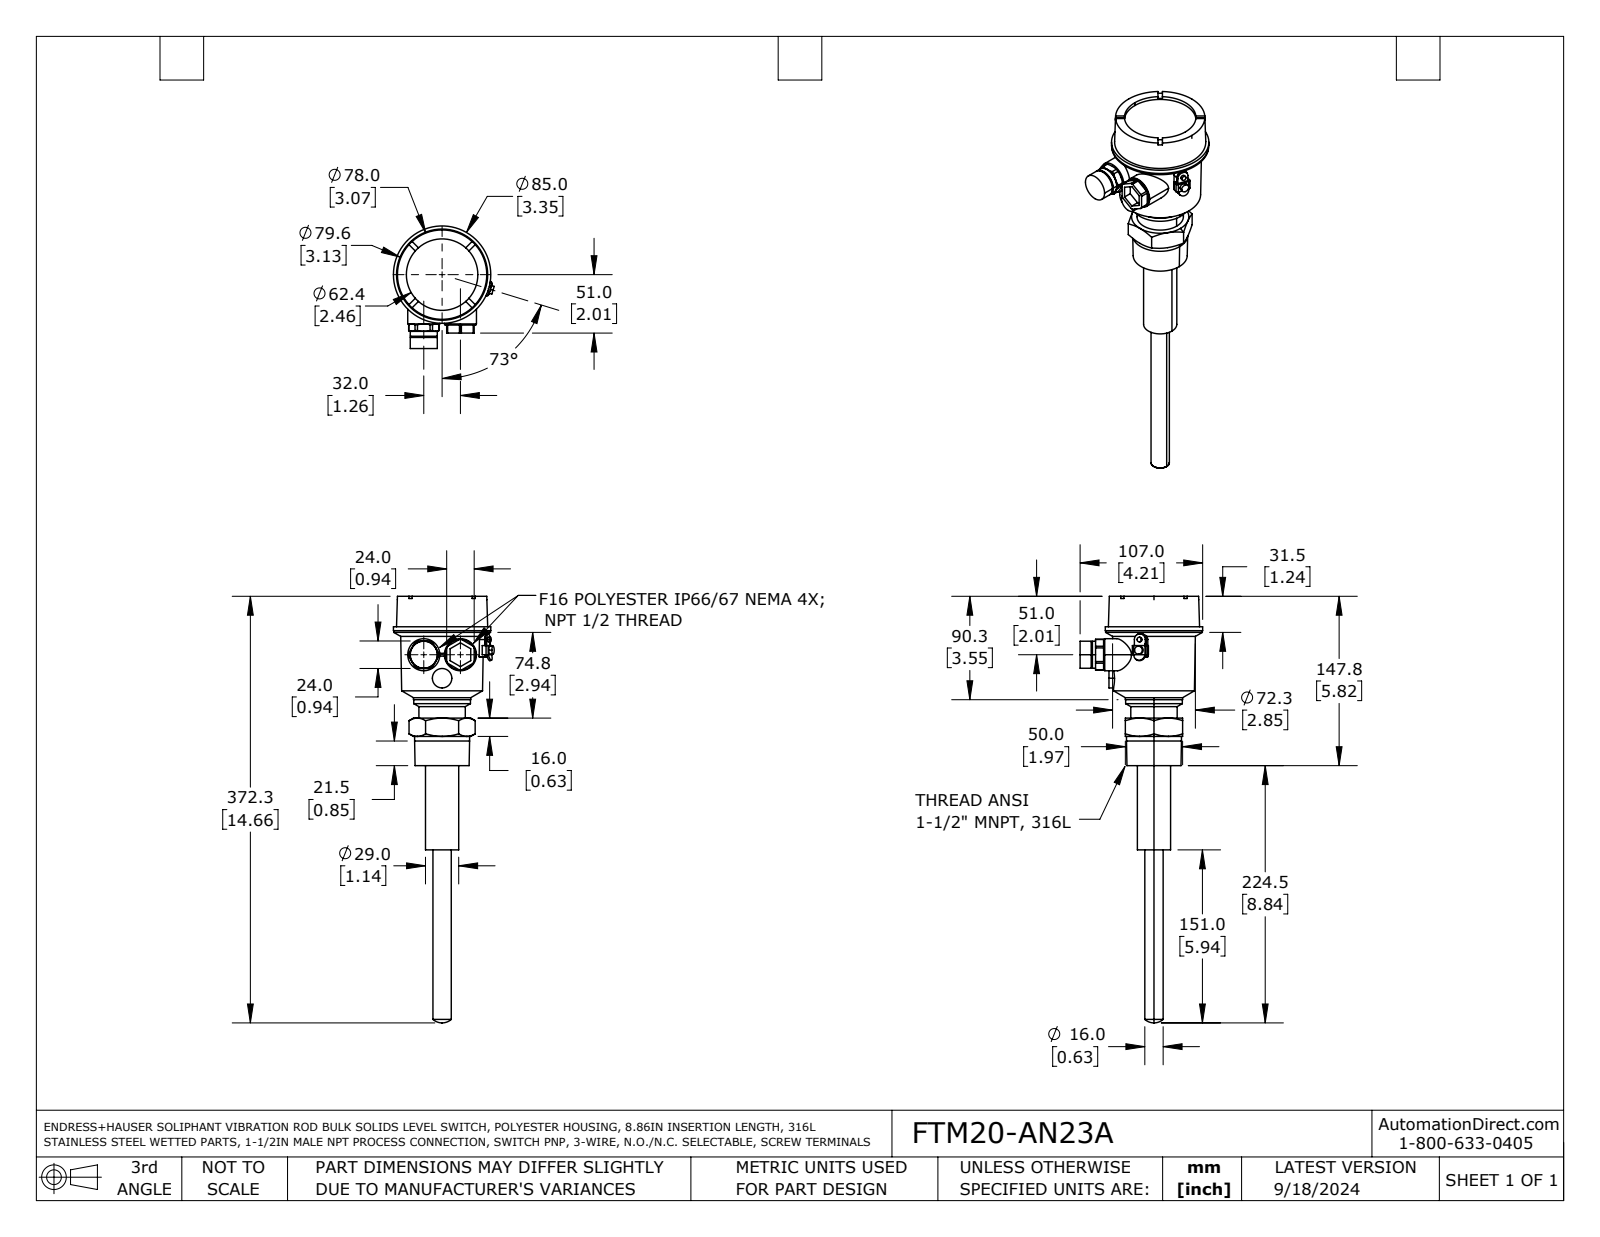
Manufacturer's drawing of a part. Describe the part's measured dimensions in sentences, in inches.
The part is named "FTM20-AN23A". Its 3-D file was written by "SolidWorks 2021 (AUTOMOTIVE_DESIGN)". It is 1 solid with 223 faces: 113 planar, 56 cylindrical and 54 other. Overall it measures 14.657 by 4.213 by 3.464 inches. Its volume is 35.84 cubic inches and its surface area 94.94 square inches. Round holes: 1 of diameter 2.457. Round bosses or shafts: 2 of diameter 1.102, 1 of diameter 3.346, 1 of diameter 3.327, 1 of diameter 1.969, 1 of diameter 1.949, 1 of diameter 1.89, 1 of diameter 1.594, 1 of diameter 1.142. Partial cylindrical surfaces (rounded edges, fillets, slot ends): 3 of radius 0.059, 1 of radius 0.197, 1 of radius 0.52. The main face-to-face distances are 0.118, 1.969, 5.701, 5.819, 4.772, 0.929, 1.047, 1.634, 3.138, 4.067.
